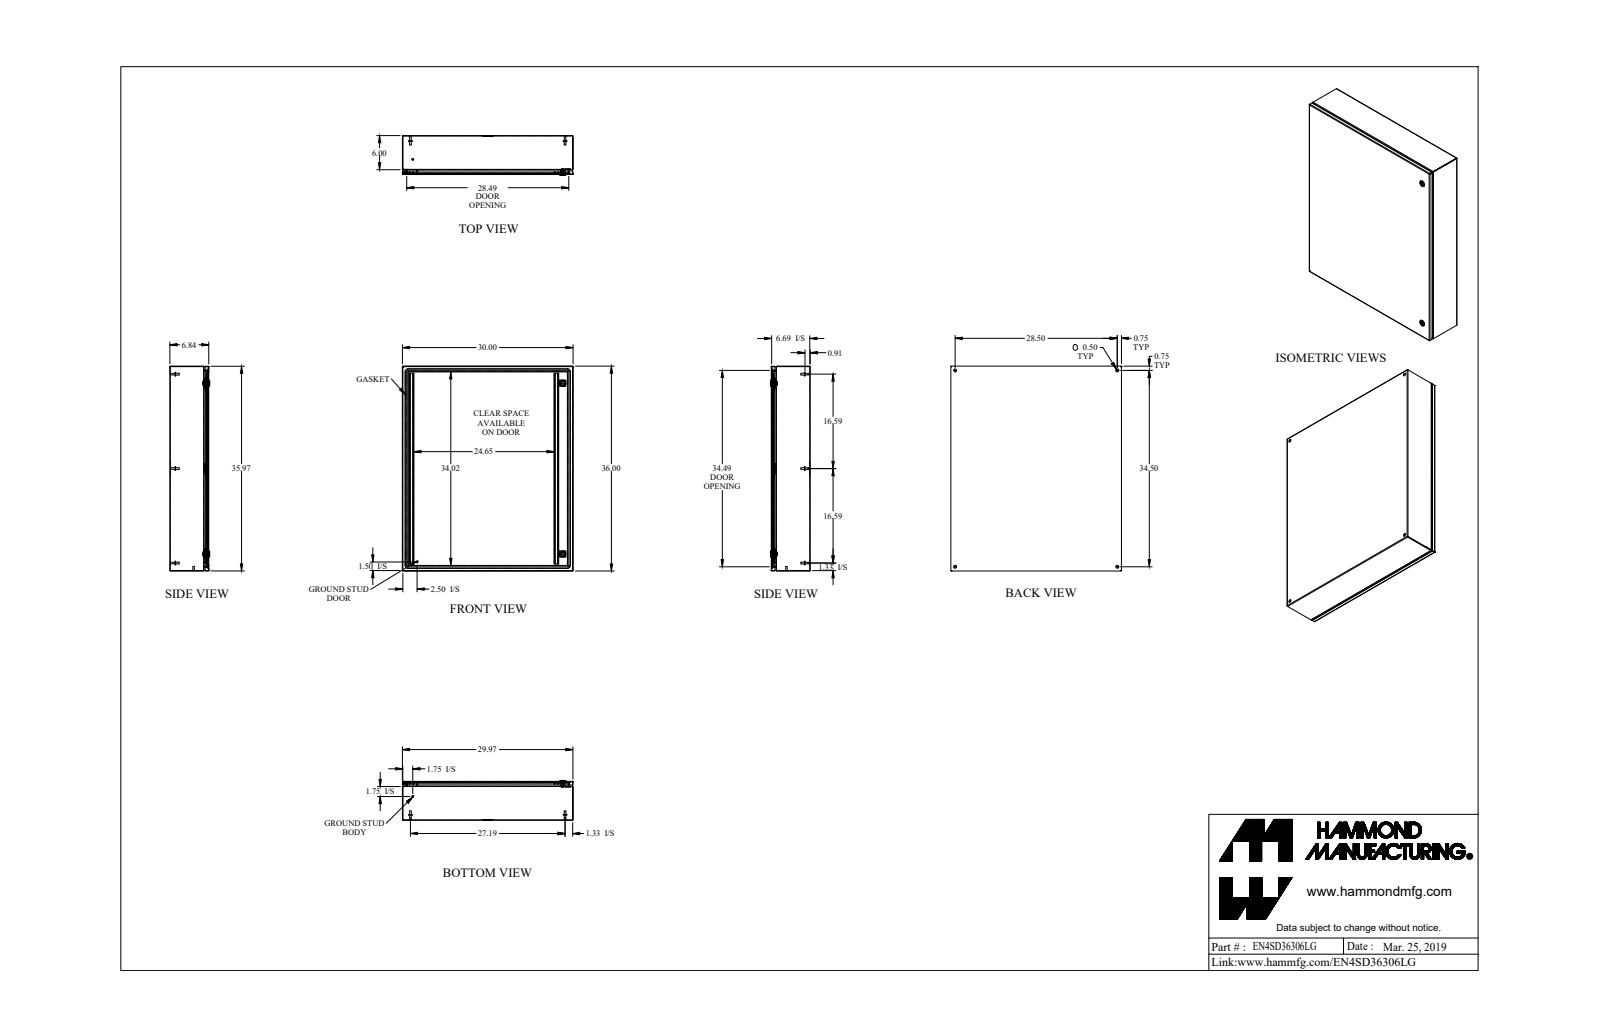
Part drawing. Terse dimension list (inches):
name: EN4SD36306LG_Default
written by: SolidWorks 2019 (CONFIG_CONTROL_DESIGN)
unit: in
bodies: 33 solids, 909 faces (430 planar, 295 cylindrical, 184 other)
size: 36 × 30 × 6.997
volume: 248.7 in³; area: 6 974 in²
holes: 4× ⌀0.5, 2× ⌀0.232, 2× ⌀0.625, 2× ⌀0.785, 1× ⌀0.172, 1× ⌀0.24, 1× ⌀0.242
bosses: 6× ⌀0.625, 6× ⌀0.313, 6× ⌀0.27, 2× ⌀1.1, 2× ⌀0.525, 2× ⌀0.281, 2× ⌀0.25, 1× ⌀0.455
rounds: 20× R0.036, 20× R0.108, 12× R0.043, 12× R0.081, 10× R0.312, 6× R0.006, 6× R0.062, 4× R0.125
face distances: 0.072, 6.765, 6.693, 6.837, 29.928, 35.928, 29.856, 30, 35.856, 36
hole spacings: 27.519, 28.5, 34.5, 44.749, 2.493, 2.494, 29.999, 32.267
